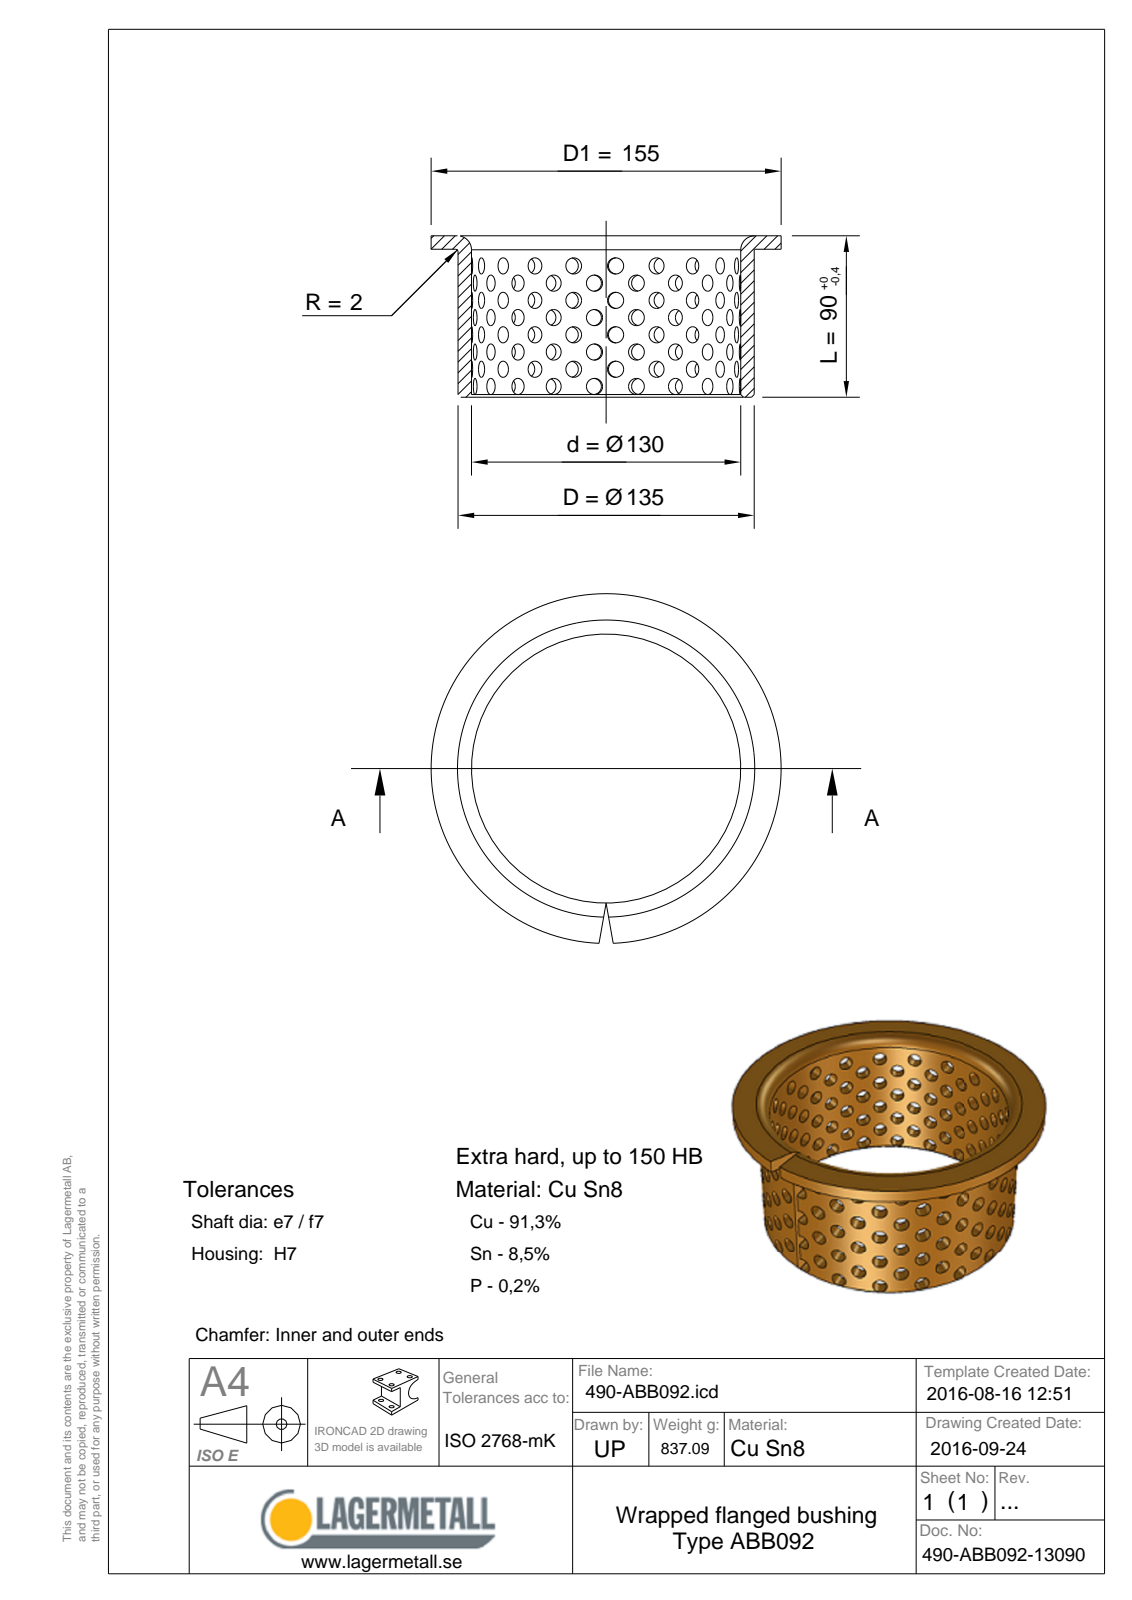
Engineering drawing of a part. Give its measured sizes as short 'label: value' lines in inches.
written by: Spatial InterOp 3D (CONFIG_CONTROL_DESIGN)
unit: in
bodies: 1 solid, 26 faces (5 planar, 9 cylindrical, 12 other)
size: 6.102 × 6.102 × 3.543
volume: 6.306 in³; area: 132.1 in²
holes: 1× ⌀5.118
bosses: 1× ⌀6.102, 1× ⌀5.315
face distances: 0.098, 3.445, 3.543
